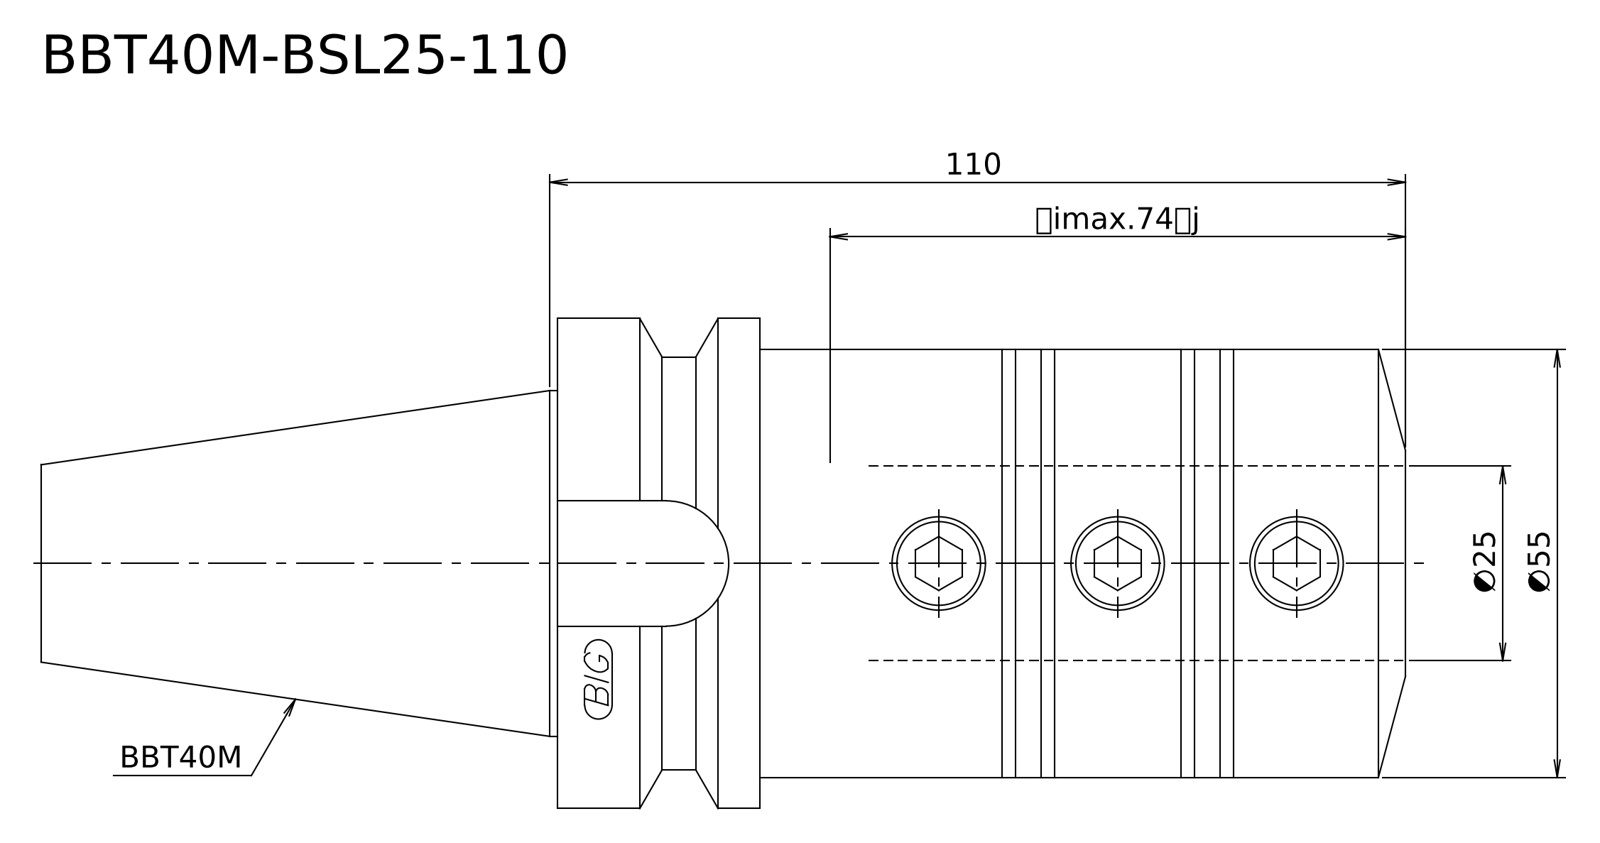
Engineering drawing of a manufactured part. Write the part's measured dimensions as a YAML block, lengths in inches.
step_written_by: "Kubotek KeyCreator V8.5.1 (14335) (CONFIG_CONTROL_DESIGN)"
units: inches
bodies: {solids: 1, faces: 13, planar: 4, cylindrical: 5, other: 4}
overall_size: [6.906, 2.48, 2.48]
volume: 20.39
surface_area: 50.15
round_bosses_or_shafts:
  - {diameter: 2.48, count: 1}
  - {diameter: 2.165, count: 1}
  - {diameter: 2.087, count: 1}
  - {diameter: 1.75, count: 1}
face_to_face_distances: [1.024, 3.268, 4.291, 6.906, 3.638, 2.614]
